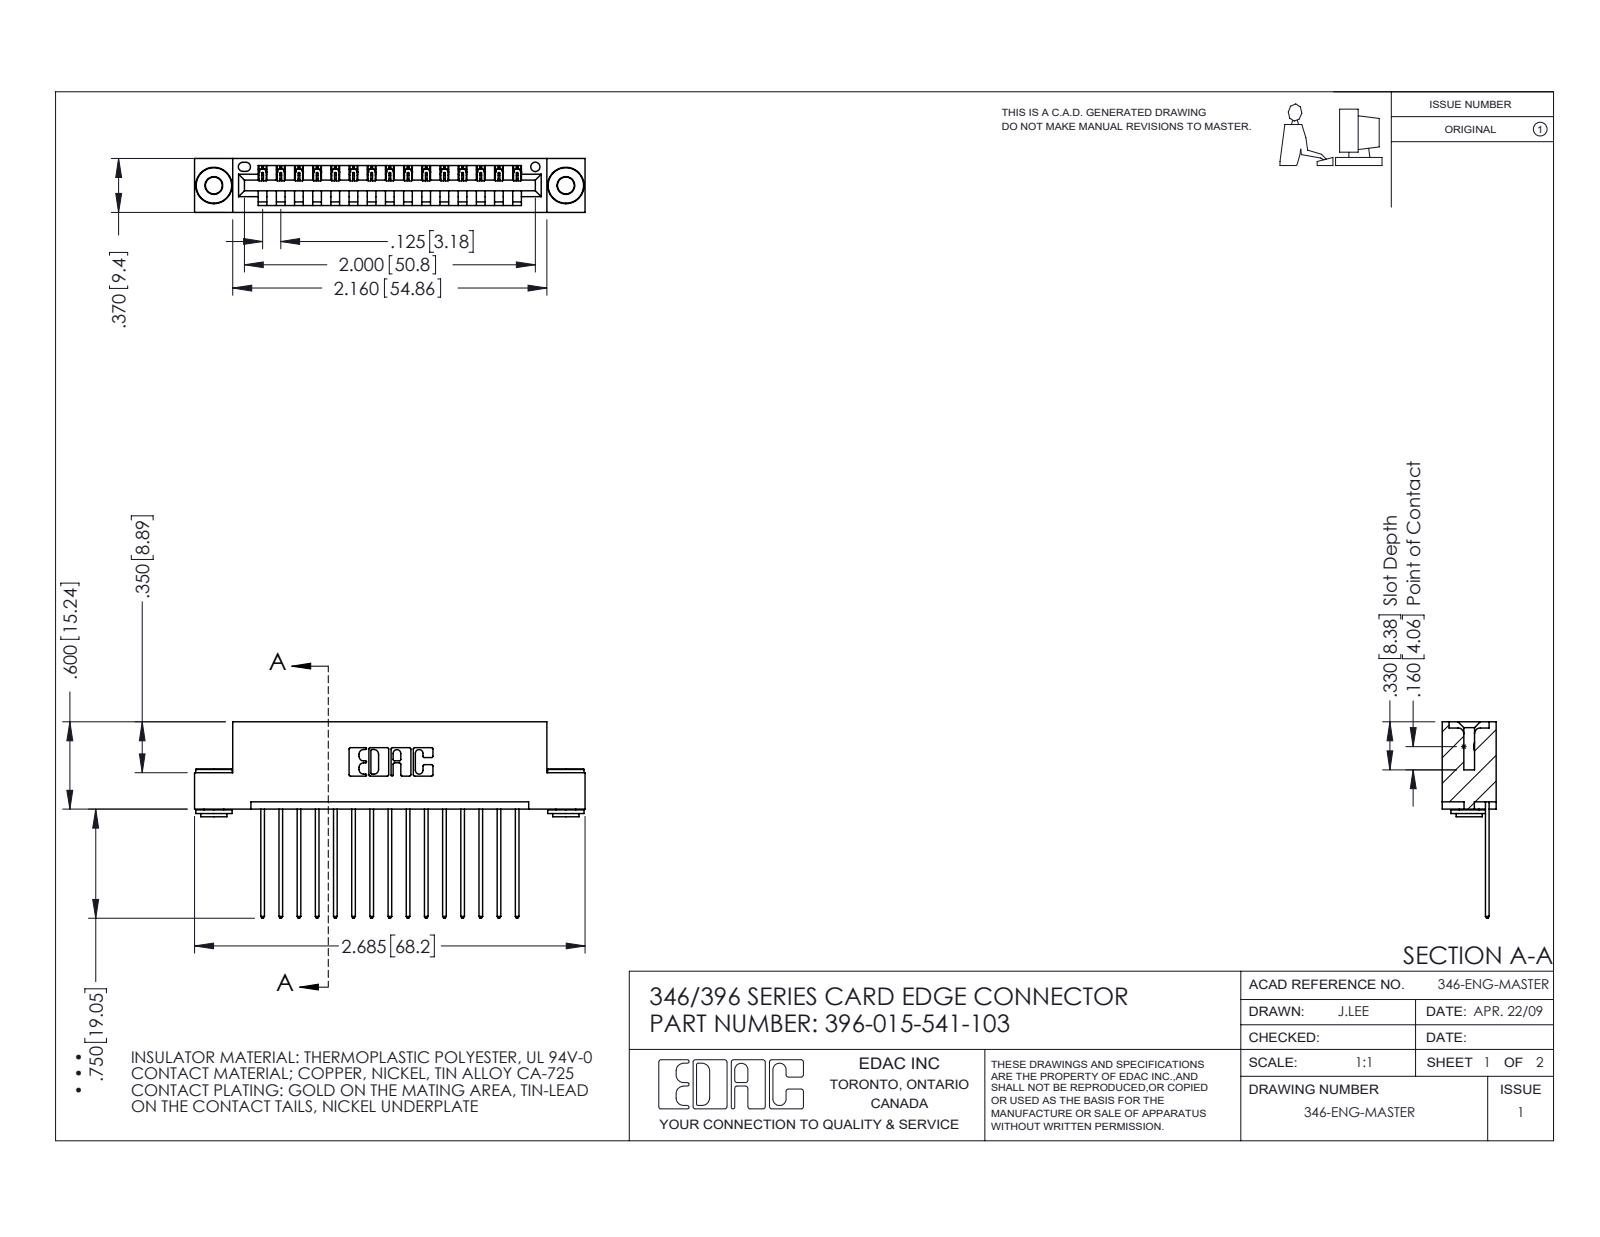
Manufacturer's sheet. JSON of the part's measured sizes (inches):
{"part_name": "345-250-002_345-250-002-102; 345-292-001_345-293-141; 346 Part_Flush Mounting Lugs - 0.156 Dia-TH; 396-015-541-103", "step_written_by": "SolidWorks 2016 (CONFIG_CONTROL_DESIGN)", "units": "inches", "bodies": {"solids": 18, "faces": 1030, "planar": 686, "cylindrical": 336, "other": 8}, "overall_size": [2.685, 1.35, 0.37], "volume_in3": 0.391, "surface_area_in2": 12.77, "round_holes": [[0.116, 2], [0.156, 2], [0.064, 1]], "round_bosses_or_shafts": [[0.25, 2], [0.18, 2], [0.136, 2]], "partial_cylinders_radius": [[0.006, 30], [0.01, 30], [0.01, 22], [0.007, 6], [0.031, 6], [0.026, 3], [0.031, 2], [0.04, 2]], "face_to_face_distances": [0.048, 0.322, 0.25, 0.37, 0.025, 0.072, 0.298, 0.148, 0.222, 0.1], "hole_center_spacings": [0.246, 2.213, 2.42]}
